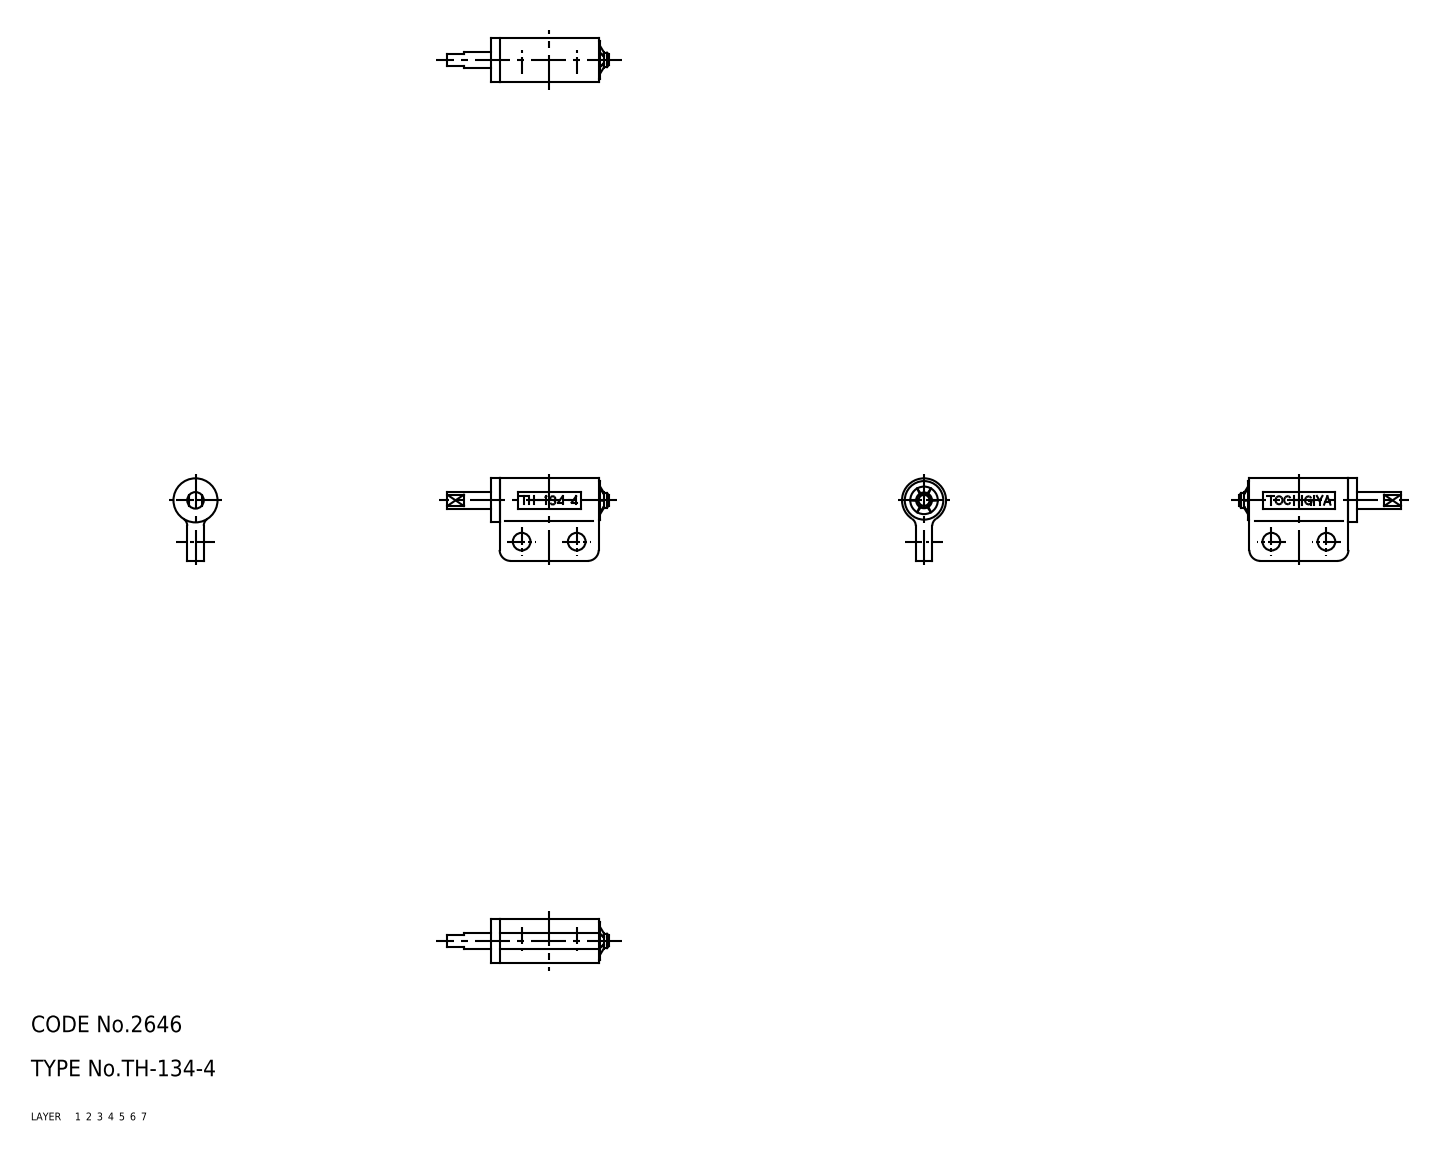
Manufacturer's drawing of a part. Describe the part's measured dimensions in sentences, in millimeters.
The part is named "shaft; retainer; case; TH_134_4_4137_36". Its 3-D file was written by "CADfix (AUTOMOTIVE_DESIGN)". It is 3 solids with 81 faces: 0 planar, 0 cylindrical and 81 other. Overall it measures 29.3 by 15 by 8 millimeters. Its volume is 1 004 cubic millimeters and its surface area 1 630 square millimeters.
